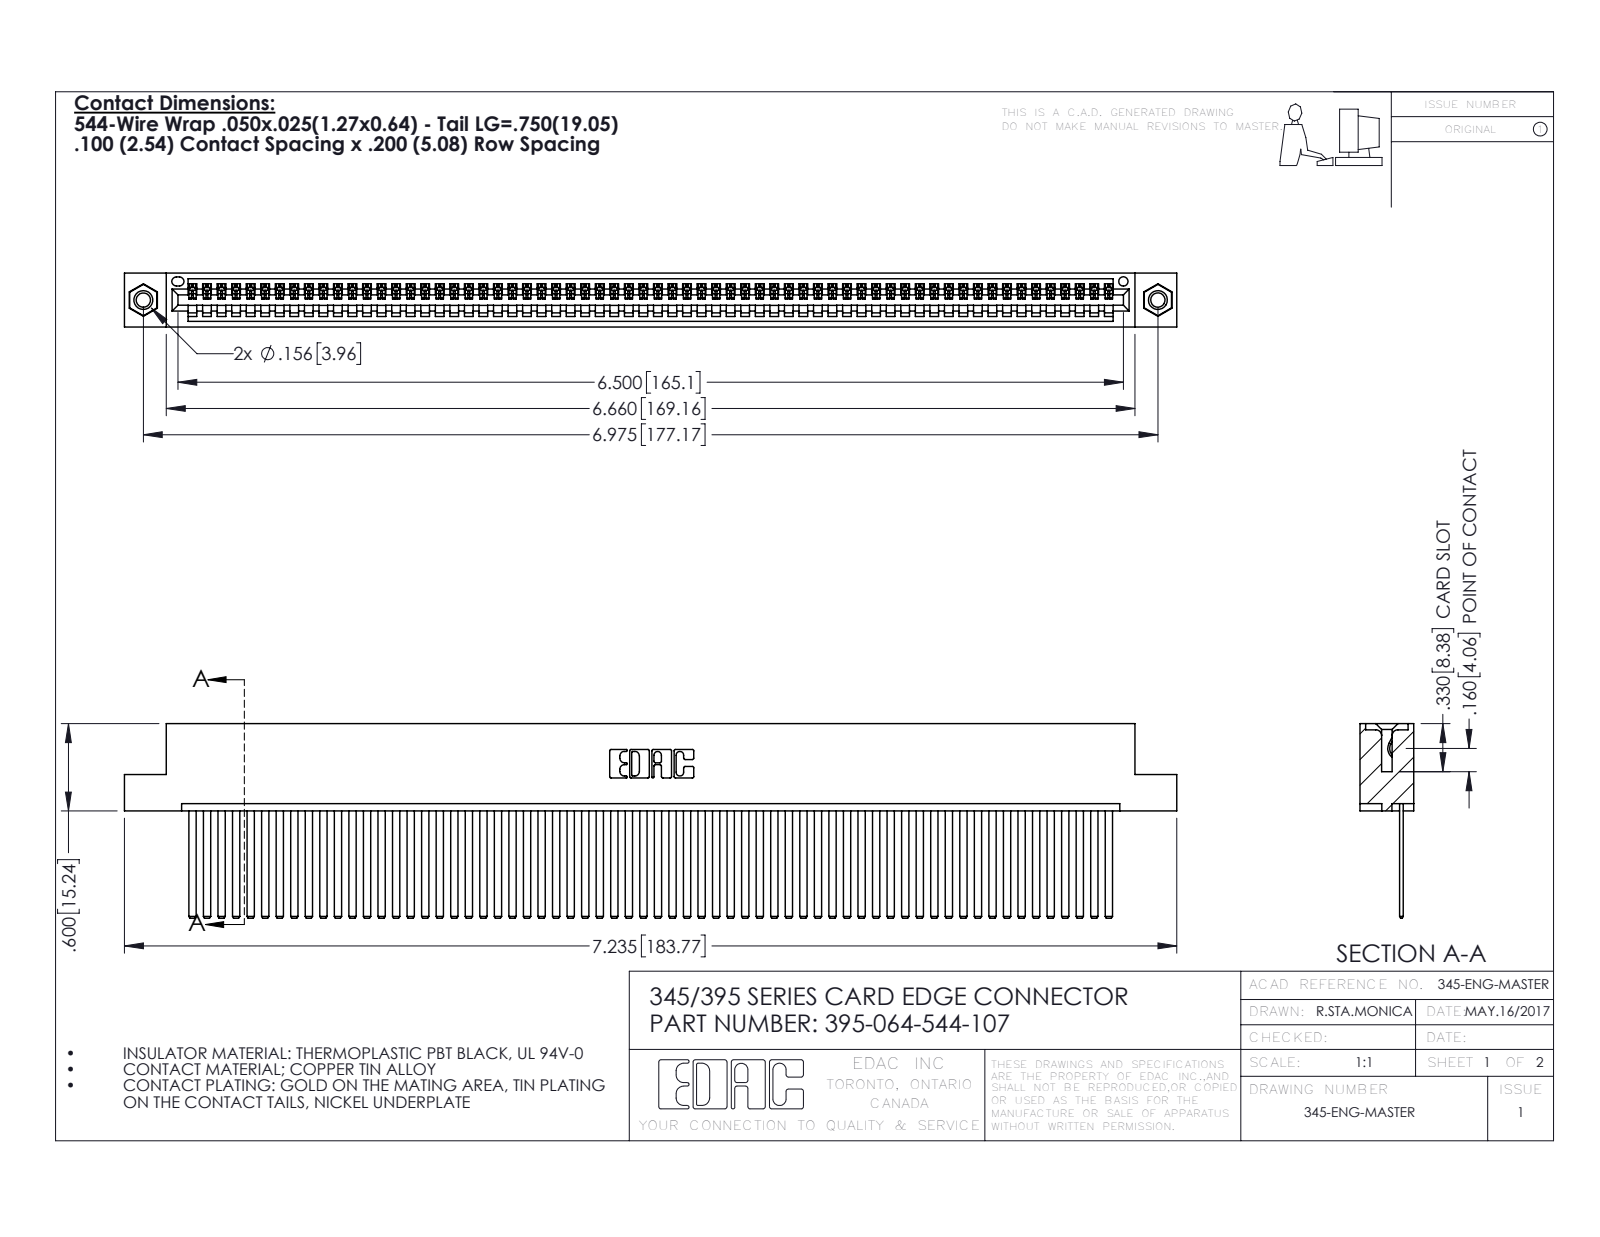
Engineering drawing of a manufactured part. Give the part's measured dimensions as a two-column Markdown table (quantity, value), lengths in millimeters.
| quantity | value |
| --- | --- |
| part name | 345-250-001_345-250-005-103; 345 Part_Flush Mounting Lugs - 0.156 Dia-TI; 345-292-001_345-293-144; 395-064-544-107 |
| STEP written by | SolidWorks 2016 (CONFIG_CONTROL_DESIGN) |
| units | millimeters |
| bodies | 67 solids, 3514 faces (2416 planar, 1082 cylindrical, 16 other) |
| overall size | 183.8 × 34 × 9.4 |
| volume | 18 370 mm³ |
| surface area | 26 960 mm² |
| round holes (diameter × count) | 2.5 × 2, 3.2 × 2, 4 × 2, 1.6 × 1 |
| round bosses / shafts (diameter × count) | 3.9 × 2 |
| partial cylindrical surfaces (radius × count) | 0.2 × 128, 0.3 × 22, 0.2 × 6, 0.8 × 6, 0.7 × 3, 0.8 × 2, 1 × 2, 0.4 × 1 |
| main face-to-face distances | 1.8, 7.6, 0.6, 2.5, 6.9, 9.4, 5.1, 5.7, 3.8, 1.8 |
| hole center spacings | 6.9, 171.2, 177.2 |
